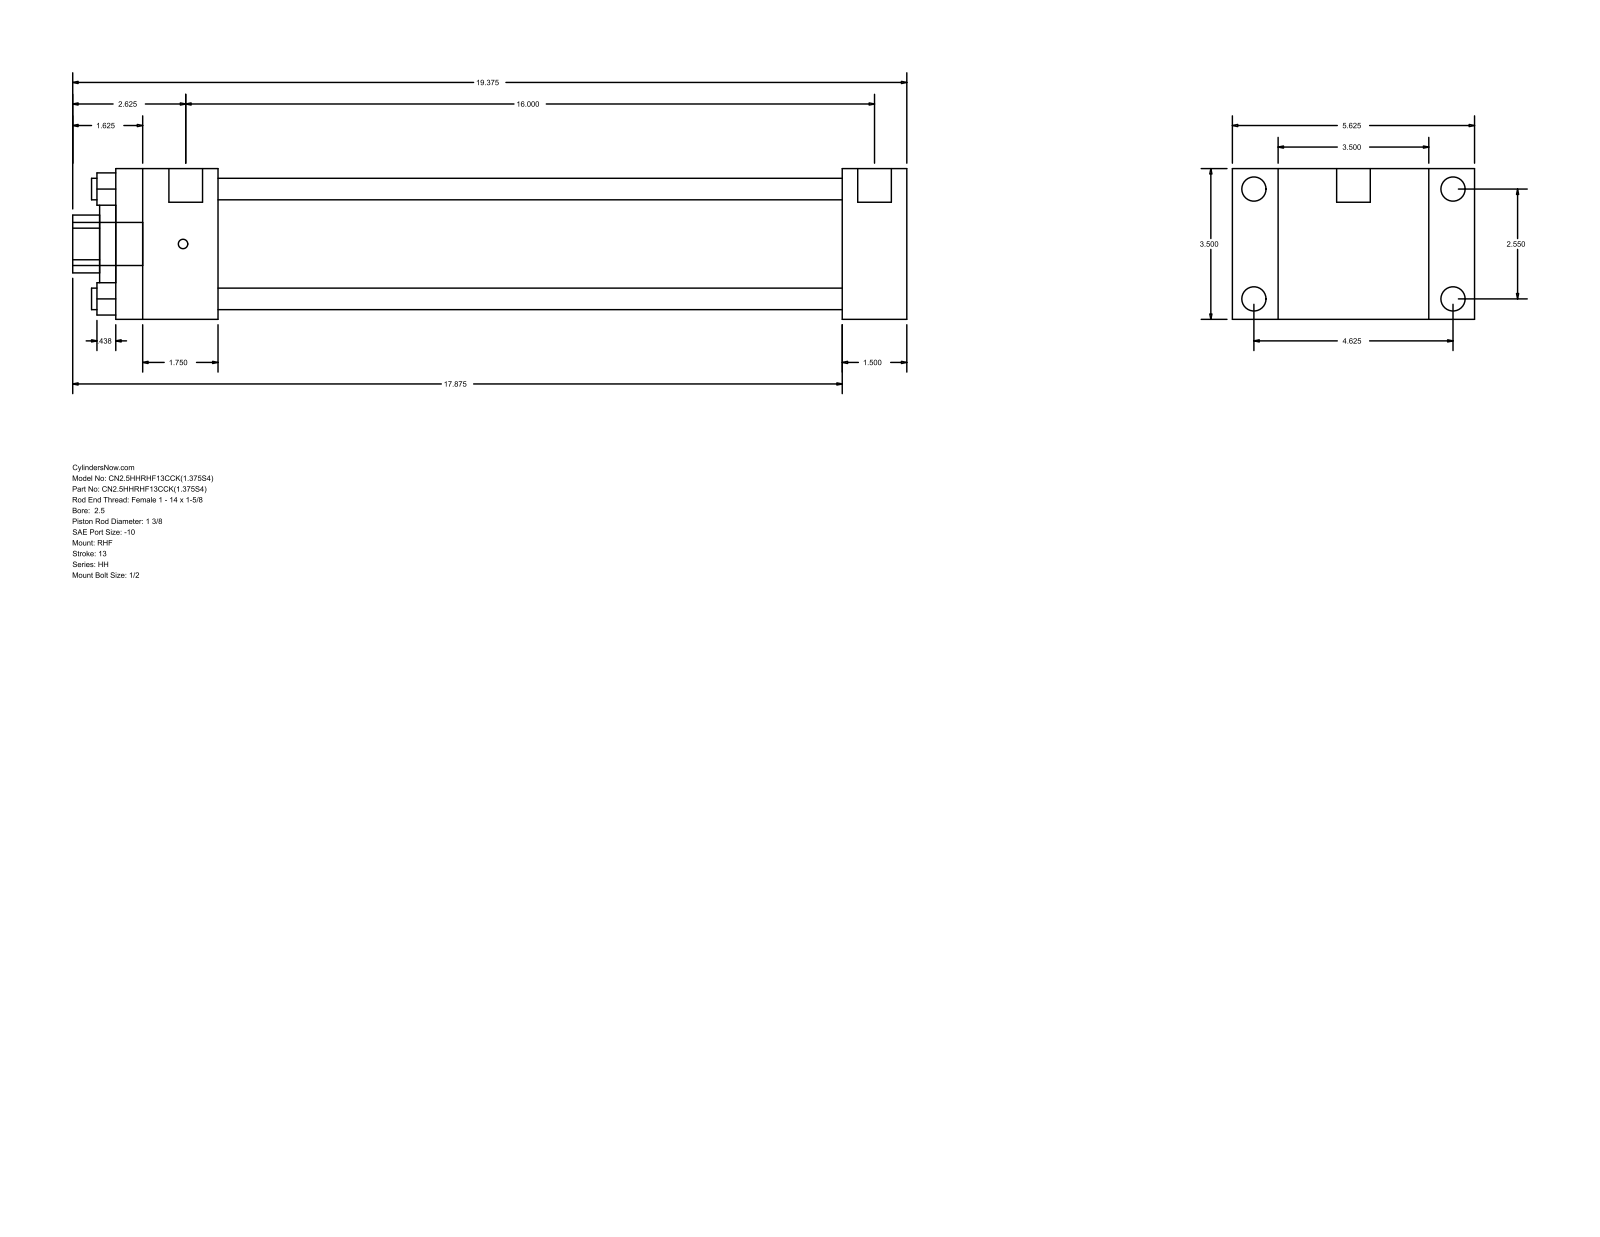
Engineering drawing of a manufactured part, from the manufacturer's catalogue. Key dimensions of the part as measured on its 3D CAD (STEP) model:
Part name (STEP PRODUCT): HH_RHF__0250_1.375
STEP written by: GSSL Pune (CONFIG_CONTROL_DESIGN)
Units: millimetres
Bodies: 0 solids, 88 faces (60 planar, 28 cylindrical, 0 other)
Overall size (bounding box): 492.12 × 142.88 × 88.9
Round holes (diameter × count): ⌀12.7 ×4, ⌀34.92 ×1, ⌀50.8 ×1, ⌀73.03 ×1
Round bosses / shafts (diameter × count): ⌀14.3 ×4, ⌀5.56 ×4, ⌀19.84 ×2, ⌀25.4 ×1
Partial cylindrical surfaces — rounded edges, fillets, slot ends (radius × count): R17.06 ×1
Main face-to-face distances: 88.9, 38.1, 26.99, 115.89, 428.62, 466.72, 142.88, 60.32, 368.3, 406.4
Hole centre spacings: 45.79, 64.76, 91.58
